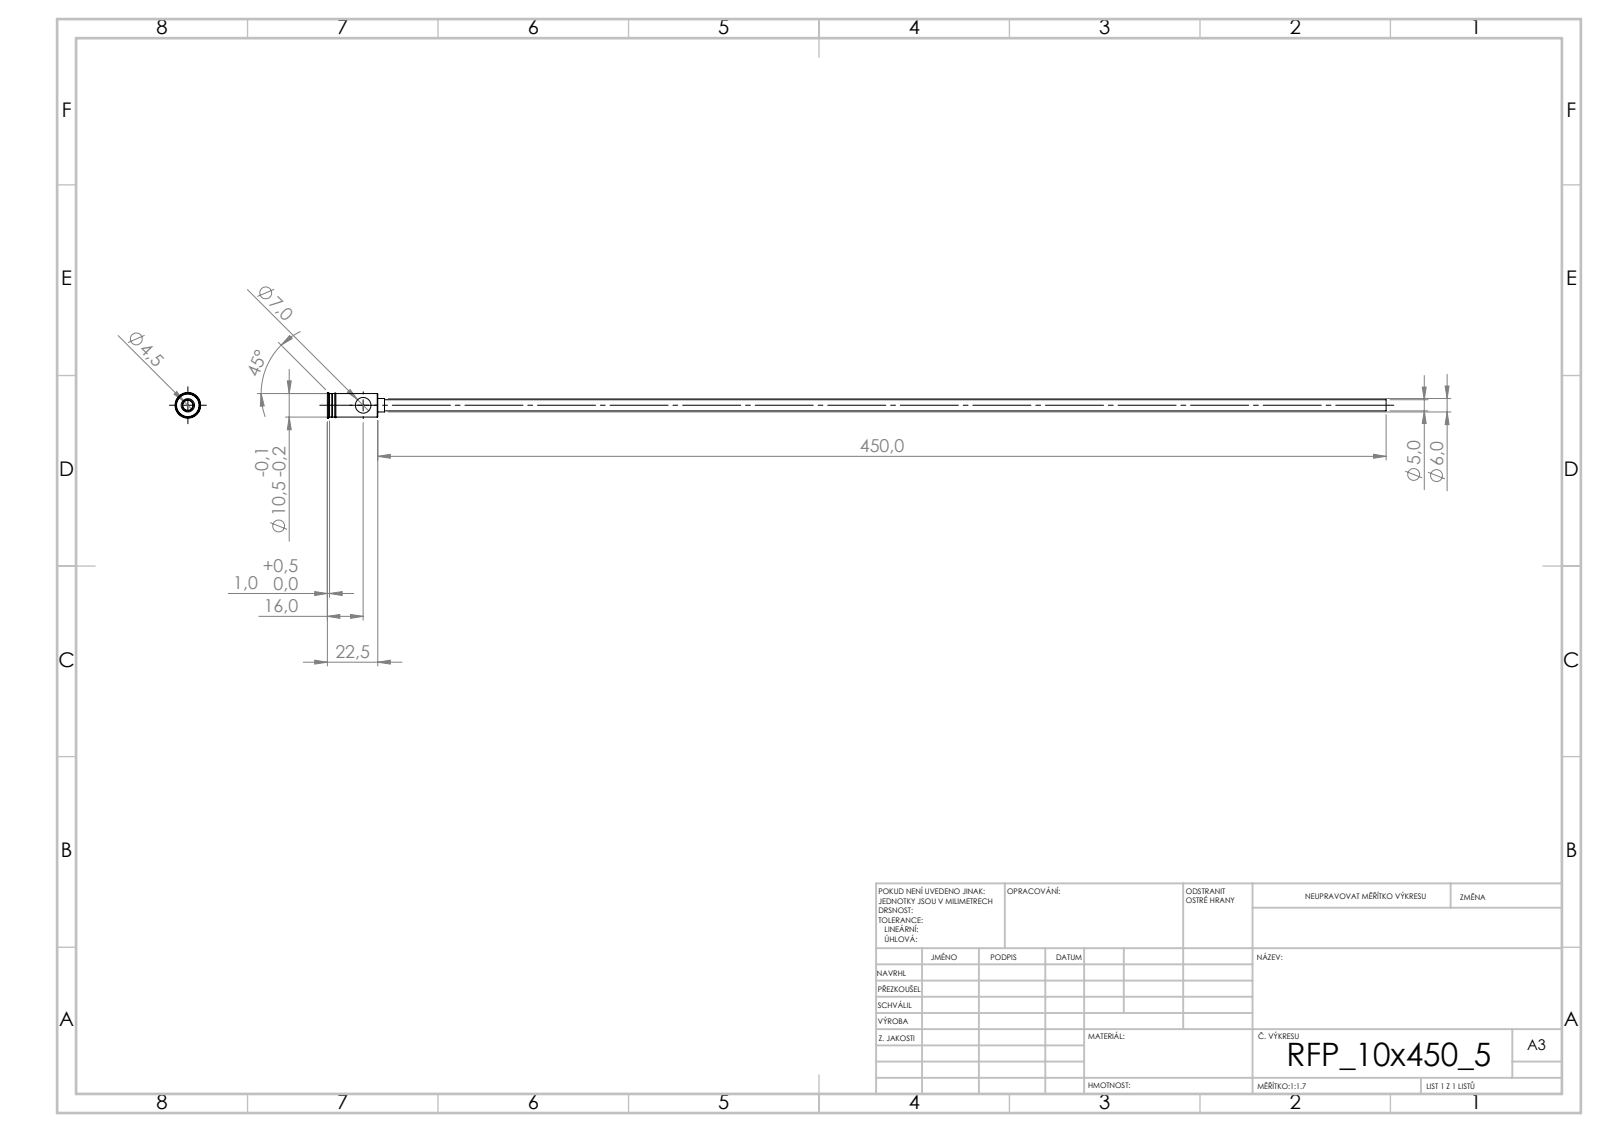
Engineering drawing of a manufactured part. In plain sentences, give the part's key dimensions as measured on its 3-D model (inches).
Its 3-D file was written by "SolidWorks 2019 (CONFIG_CONTROL_DESIGN)". It is 1 solid with 44 faces: 20 planar, 16 cylindrical and 8 other. Overall it measures 18.602 by 0.453 by 0.453 inches. Its volume is 0.194 cubic inches and its surface area 22.6 square inches. Round holes: 1 of diameter 0.177, 1 of diameter 0.276. Round bosses or shafts: 1 of diameter 0.453, 1 of diameter 0.413, 1 of diameter 0.236, 1 of diameter 0.197. The main face-to-face distances are 0.886, 0.807, 0.079, 0.232, 0.795, 0.091, 0.118, 0.913, 0.925, 1.004.
